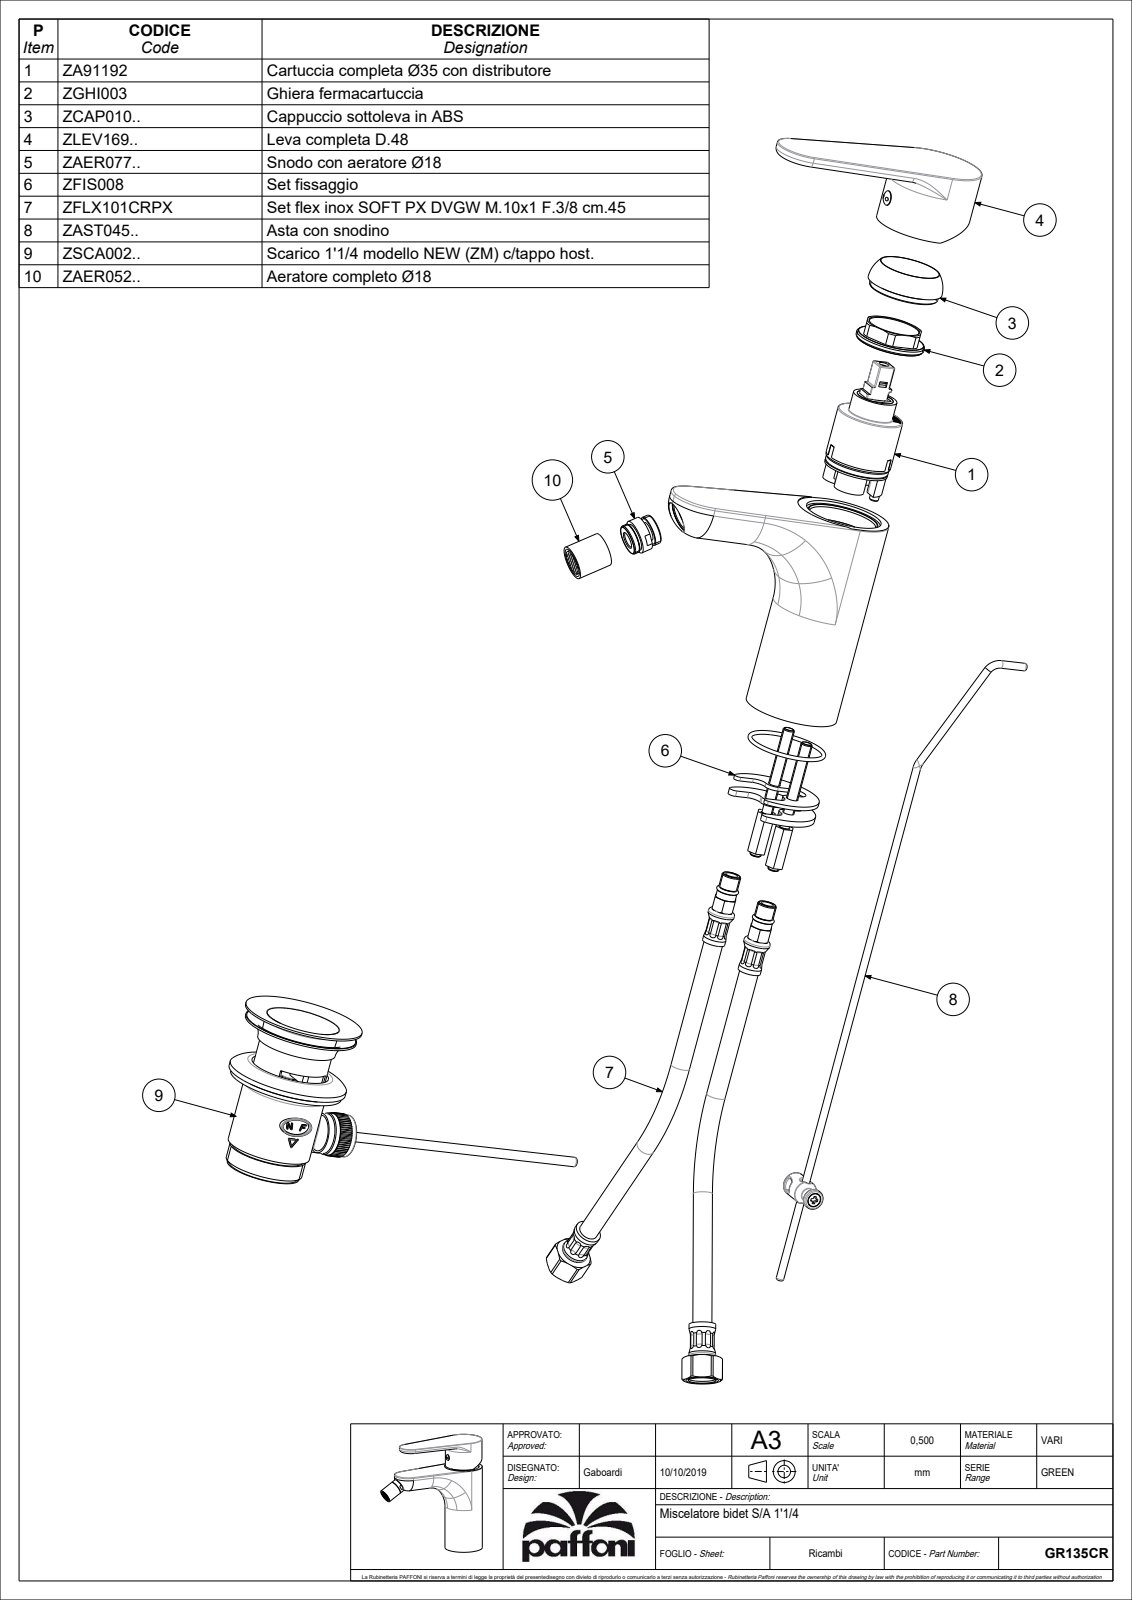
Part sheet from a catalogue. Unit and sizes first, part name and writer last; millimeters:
Units: millimetres
Overall size (bounding box): 173.82 × 147.5 × 49
Round holes (diameter × count): ⌀5 ×3, ⌀3 ×1, ⌀3.5 ×1, ⌀4.2 ×1, ⌀8 ×1, ⌀10 ×1, ⌀13 ×1, ⌀16.7 ×1, ⌀31.5 ×1, ⌀33 ×1, ⌀34 ×1, ⌀35.7 ×1
Round bosses / shafts (diameter × count): ⌀4 ×2, ⌀49 ×1, ⌀48 ×1, ⌀38.5 ×1, ⌀18 ×1, ⌀14.5 ×1, ⌀9 ×1, ⌀7.6 ×1
Partial cylindrical surfaces — rounded edges, fillets, slot ends (radius × count): R1 ×35, R0.5 ×8, R3 ×2, R5 ×2, R15 ×1, R18.5 ×1, R25 ×1
Main face-to-face distances: 3, 37, 6, 40, 31, 2.5, 38, 34, 35, 2
Hole centre spacings: 12.3, 13.57, 13.6, 13.45, 13.5, 22
Volume: 132 611 mm³ · Surface area: 81 821 mm²
Bodies: 3 solids, 378 faces (93 planar, 132 cylindrical, 153 other)
Part name (STEP PRODUCT): GR135CR
STEP written by: CREO PARAMETRIC BY PTC INC, 2020044 (CONFIG_CONTROL_DESIGN)
